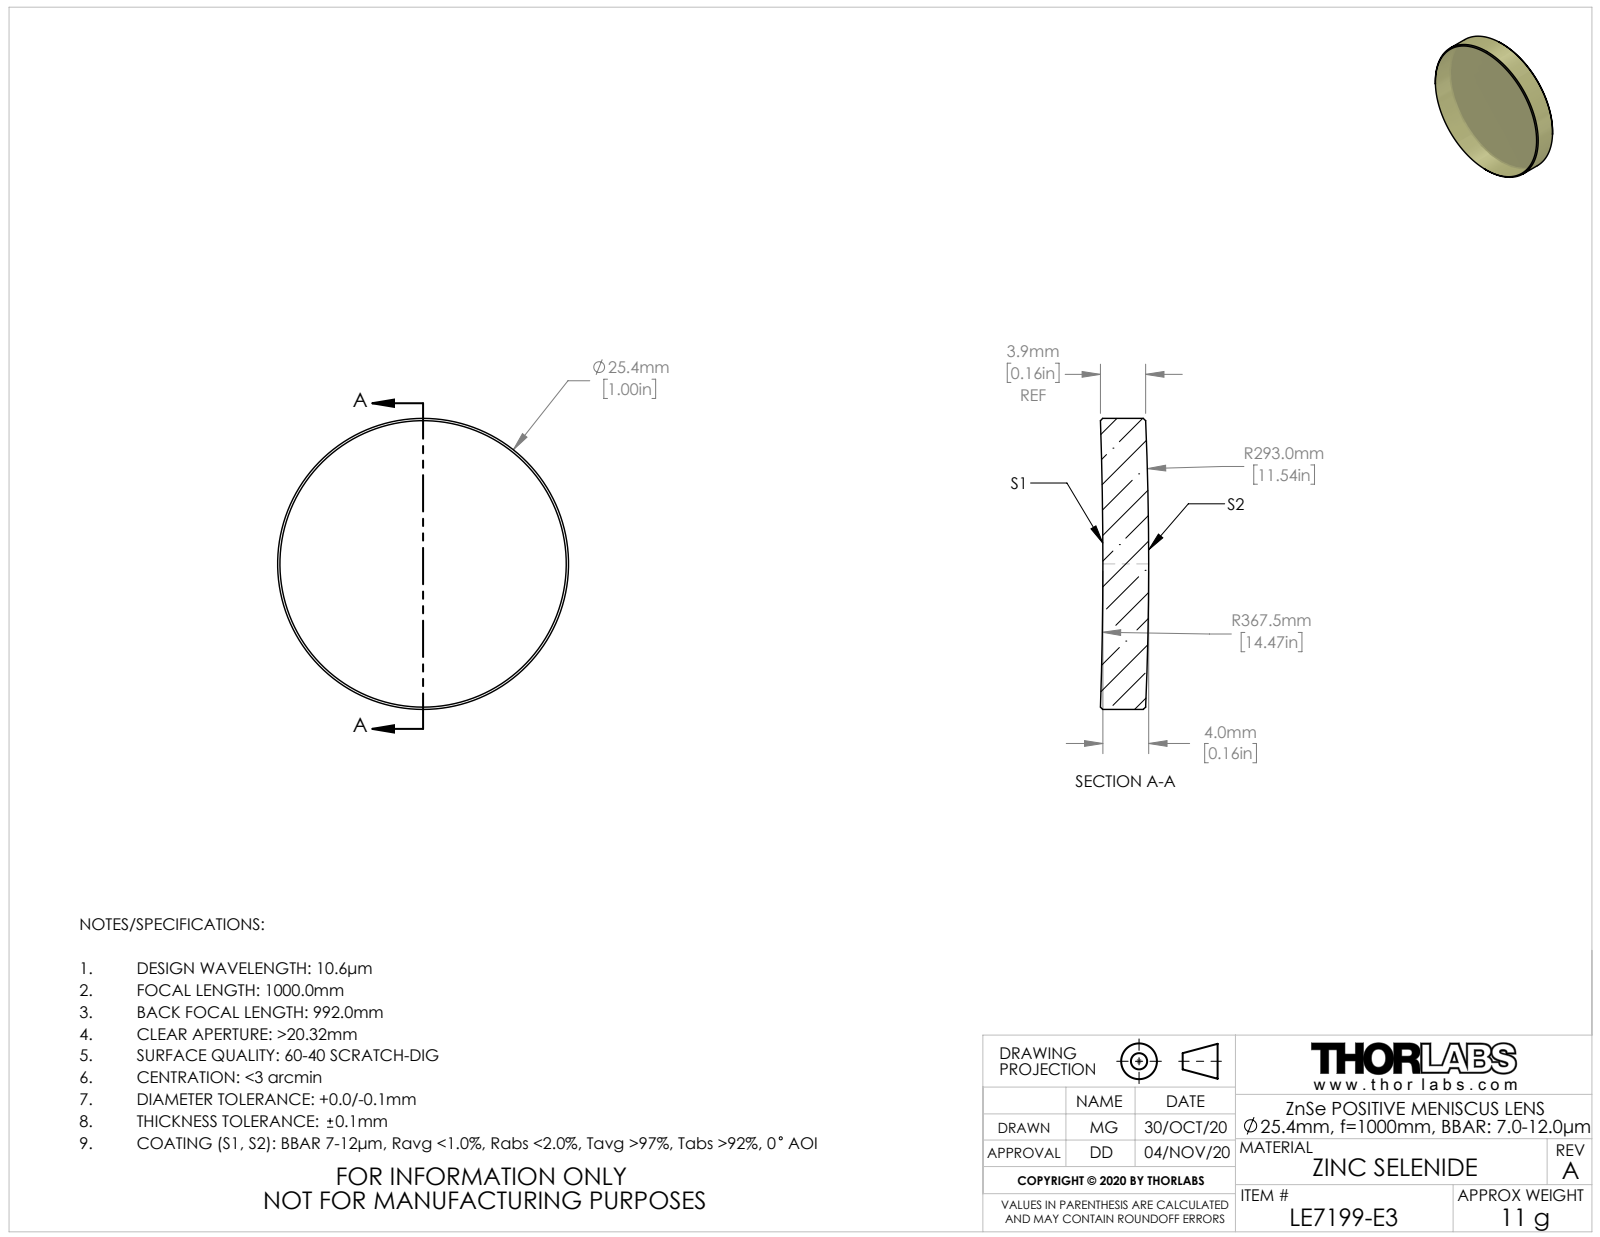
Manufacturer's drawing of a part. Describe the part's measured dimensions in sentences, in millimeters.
The part is named "TTN225635-E0W". Its 3-D file was written by "SolidWorks 2018 (CONFIG_CONTROL_DESIGN)". It is 1 solid with 10 faces: 0 planar, 2 cylindrical and 8 other. Overall it measures 25.4 by 25.4 by 4.21 millimeters. Its volume is 2 010 cubic millimeters and its surface area 1 310 square millimeters. Round bosses or shafts: 1 of diameter 25.4.
